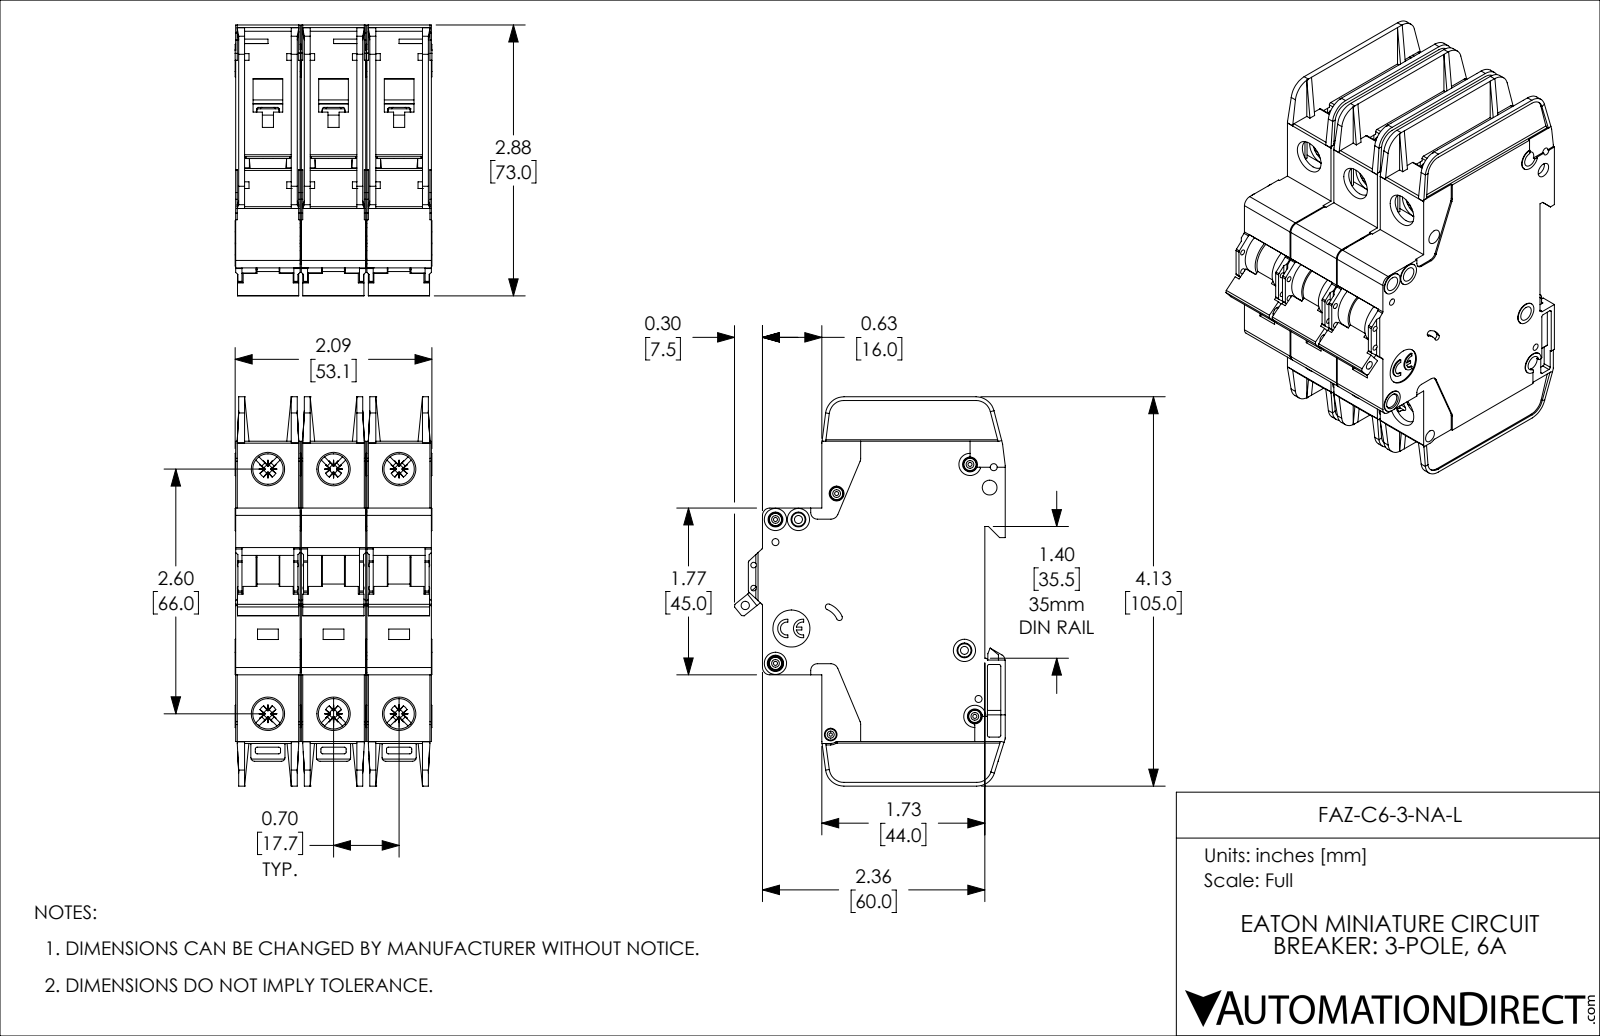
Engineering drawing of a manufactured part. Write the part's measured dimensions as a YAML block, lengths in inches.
part_name: "FAZ-C6-3-NA-L"
step_written_by: "SolidWorks 2019 (AUTOMOTIVE_DESIGN)"
units: inches
bodies: {solids: 3, faces: 3381, planar: 2013, cylindrical: 1071, other: 297}
overall_size: [4.134, 2.876, 2.091]
volume: 14.05
surface_area: 123
round_holes:
  - {diameter: 0.157, count: 8}
  - {diameter: 0.323, count: 6}
  - {diameter: 0.043, count: 5}
  - {diameter: 0.075, count: 4}
  - {diameter: 0.059, count: 2}
  - {diameter: 0.085, count: 2}
  - {diameter: 0.035, count: 1}
  - {diameter: 0.089, count: 1}
  - {diameter: 0.098, count: 1}
  - {diameter: 0.134, count: 1}
  - {diameter: 0.394, count: 1}
round_bosses_or_shafts:
  - {diameter: 0.13, count: 5}
  - {diameter: 0.236, count: 4}
  - {diameter: 0.118, count: 4}
  - {diameter: 0.098, count: 3}
partial_cylinders:
  - {radius: 0.02, count: 72}
  - {radius: 0.016, count: 30}
  - {radius: 0.039, count: 18}
  - {radius: 0.043, count: 12}
  - {radius: 0.079, count: 12}
  - {radius: 0.008, count: 6}
  - {radius: 0.01, count: 6}
  - {radius: 0.028, count: 6}
face_to_face_distances: [0.697, 0.047, 1.394, 0.685, 0.591, 1.382, 0.744, 0.65, 0.106, 0.094]
hole_center_spacings: [0.697, 2.69, 2.598, 0.244, 0.537, 0.87, 1.394, 2.948]
